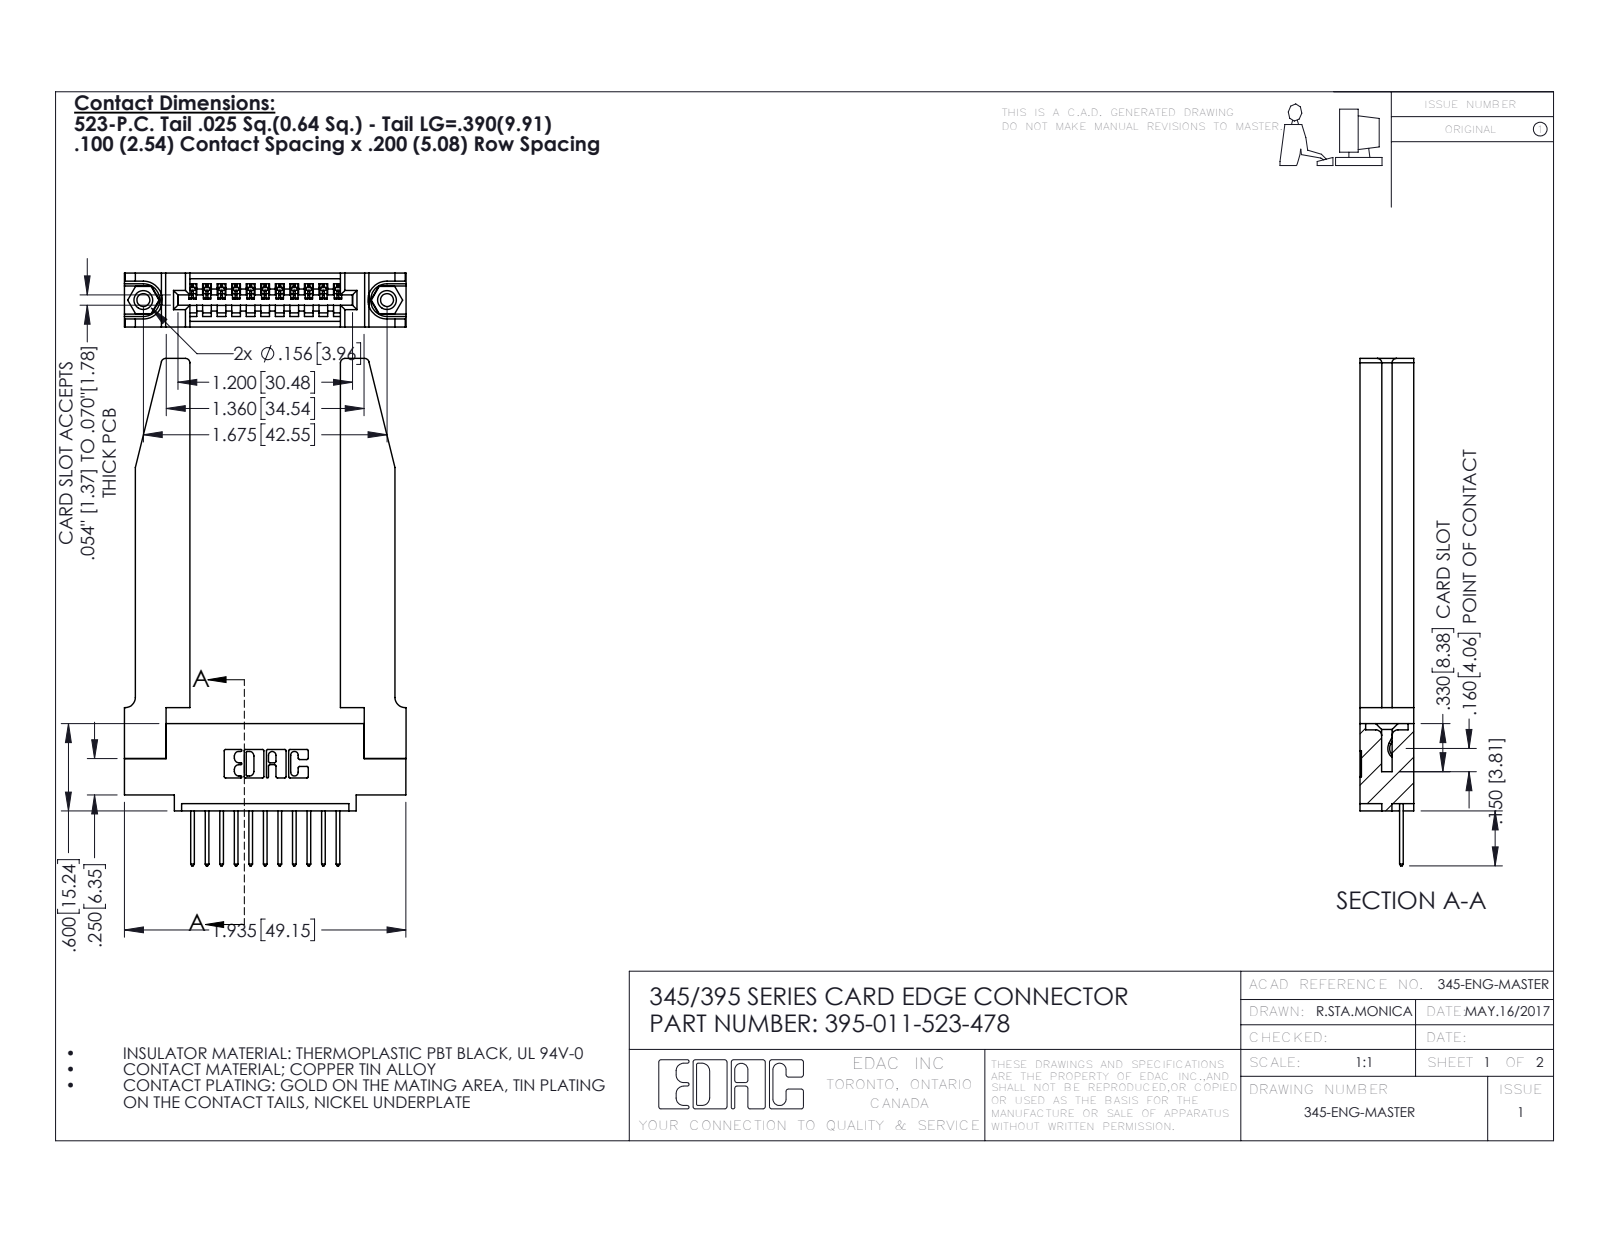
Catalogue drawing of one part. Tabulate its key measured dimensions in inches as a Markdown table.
| quantity | value |
| --- | --- |
| part name | 345-250-001_345-250-001-102; 345-220-078_345-220-078; 345 Part_0.110 Offset - 0.156 Dia-TH; 395-011-523-478 (+1 more) |
| STEP written by | SolidWorks 2016 (CONFIG_CONTROL_DESIGN) |
| units | inches |
| bodies | 16 solids, 1002 faces (666 planar, 284 cylindrical, 52 other) |
| overall size | 3.487 × 1.936 × 0.37 |
| volume | 0.739 in³ |
| surface area | 19.04 in² |
| round holes (diameter × count) | 0.089 × 2, 0.125 × 2, 0.156 × 2, 0.064 × 1 |
| round bosses / shafts (diameter × count) | 0.155 × 2 |
| partial cylindrical surfaces (radius × count) | 0.006 × 22, 0.01 × 22, 0.01 × 22, 0.03 × 8, 0.007 × 6, 0.031 × 6, 0.026 × 3, 0.031 × 2 |
| main face-to-face distances | 0.37, 0.072, 0.298, 0.148, 0.15, 0.22, 0.077, 1.035, 0.2, 0.098 |
| hole center spacings | 0.27, 1.443, 1.675 |
